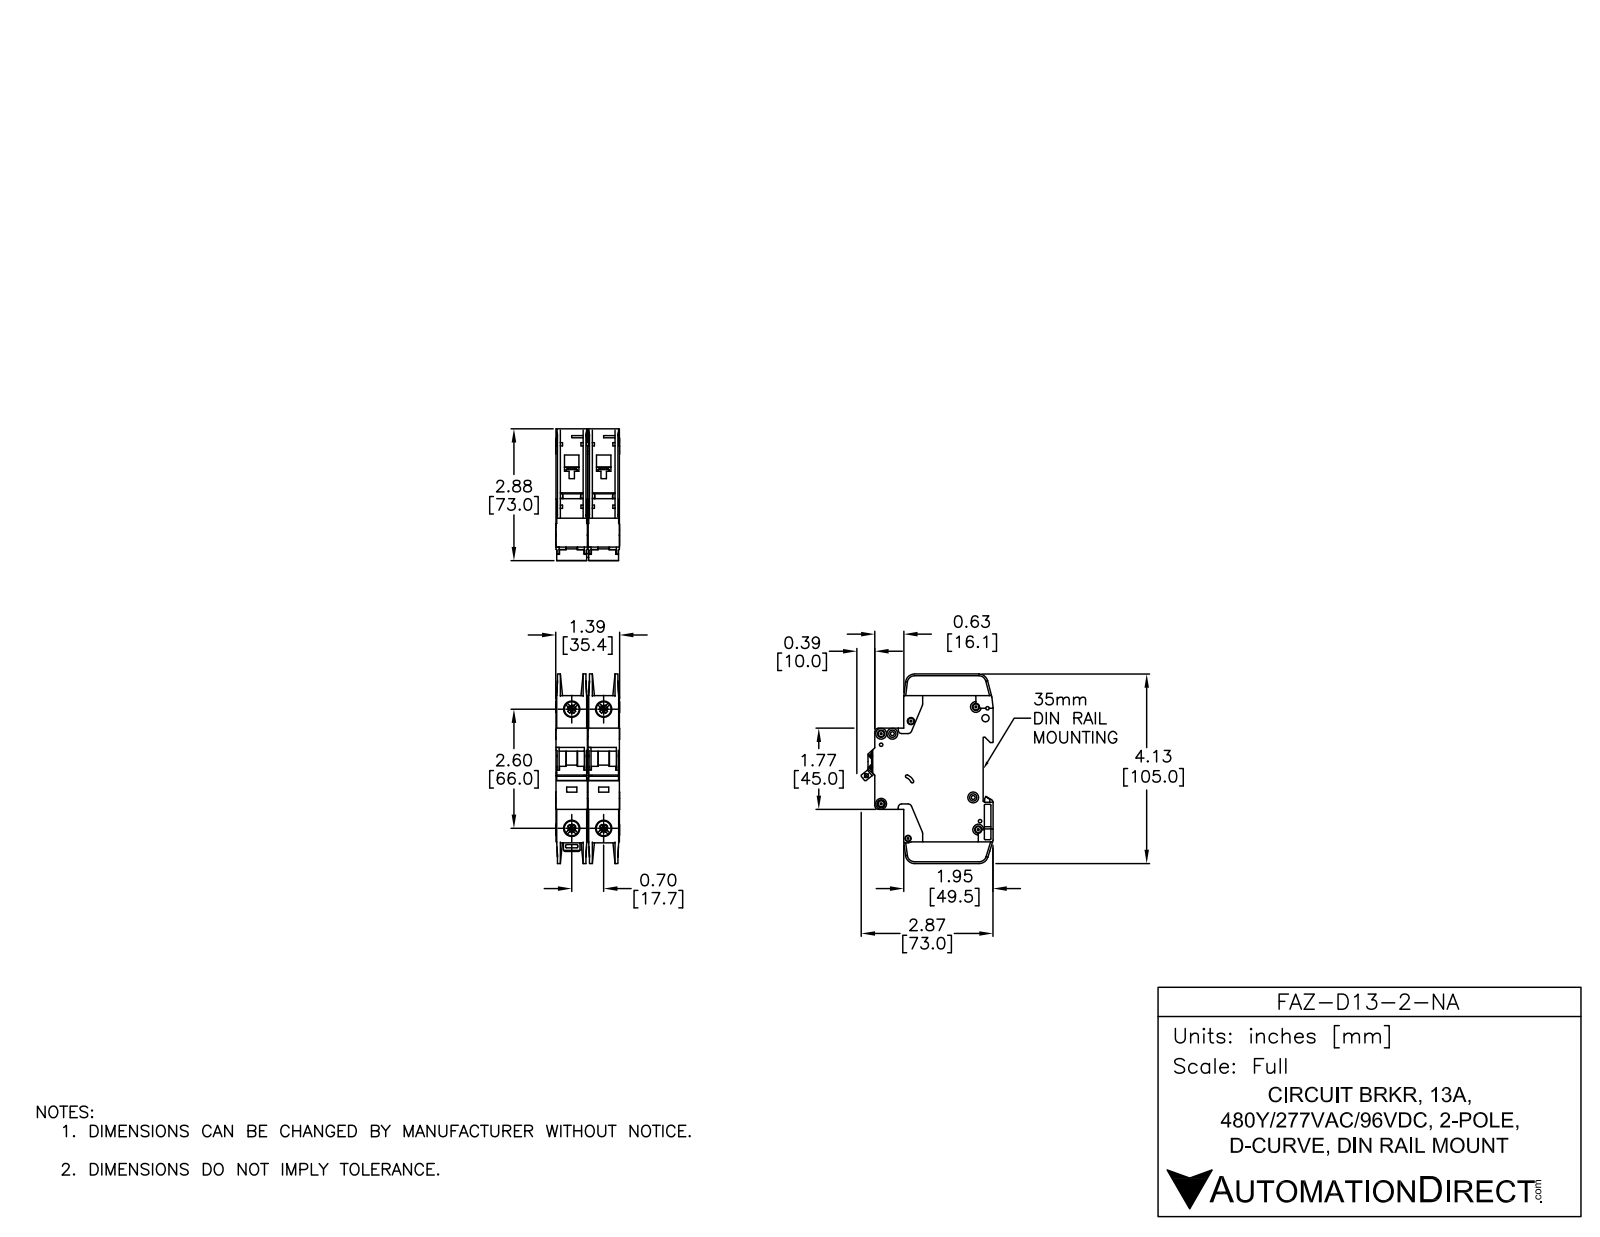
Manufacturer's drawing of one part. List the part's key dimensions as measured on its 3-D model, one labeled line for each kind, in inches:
Part name (STEP PRODUCT): FAZ-D13-2-NA
STEP written by: SolidWorks 2014 (AUTOMOTIVE_DESIGN)
Units: inches
Bodies: 6 solids, 1568 faces (818 planar, 526 cylindrical, 224 other)
Overall size (bounding box): 4.134 × 2.876 × 1.394
Volume: 9.482 in³ · Surface area: 76.69 in²
Round holes (diameter × count): ⌀0.142 ×7, ⌀0.281 ×4, ⌀0.323 ×4, ⌀0.043 ×2, ⌀0.059 ×2, ⌀0.157 ×2, ⌀0.075 ×1, ⌀0.085 ×1, ⌀0.087 ×1, ⌀0.1 ×1, ⌀0.13 ×1, ⌀0.134 ×1
Round bosses / shafts (diameter × count): ⌀0.236 ×7, ⌀0.098 ×2
Partial cylindrical surfaces — rounded edges, fillets, slot ends (radius × count): R0.01 ×47, R0.02 ×24, R0.039 ×18, R0.079 ×12, R0.197 ×5, R0.071 ×4, R0.157 ×4, R0.008 ×2
Main face-to-face distances: 0.697, 0.689, 0.028, 0.593, 0.096, 0.069, 0.62, 0.524, 1.386, 0.669
Hole centre spacings: 0.244, 0.697, 2.598, 2.69, 0.204, 0.24, 0.322, 0.337
